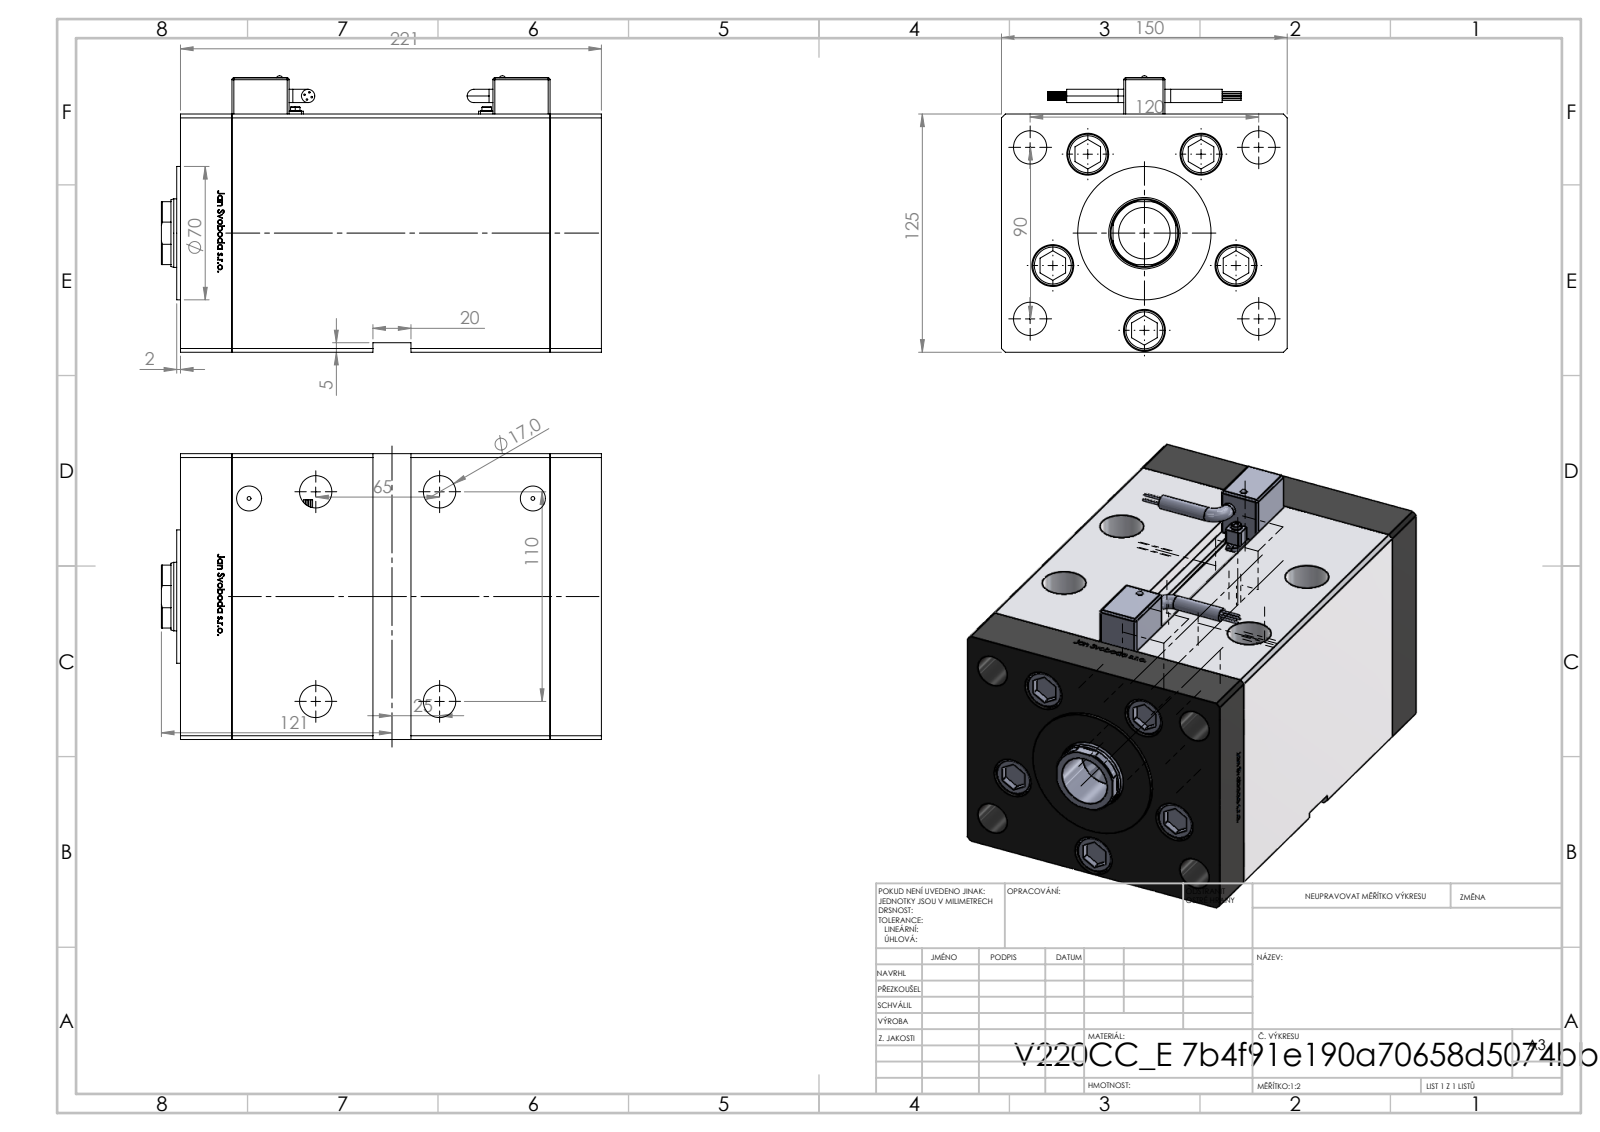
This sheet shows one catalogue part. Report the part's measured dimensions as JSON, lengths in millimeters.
{"part_name": "V220C_FRONT_E; Magnetic_Switch_MSU4; ALLEN BOLT; V220C BACK_E (+2 more)", "step_written_by": "SolidWorks 2019 (CONFIG_CONTROL_DESIGN)", "units": "millimeters", "bodies": {"solids": 16, "faces": 1410, "planar": 551, "cylindrical": 251, "other": 608}, "overall_size": [231, 150, 145.1], "volume_mm3": 3464000, "surface_area_mm2": 399924, "round_holes": [[17.5, 9], [22, 5], [17, 4], [23, 4], [2, 2], [3.6, 2], [5, 2], [7, 2], [13.16, 2], [27, 1], [36, 1], [37.5, 1]], "round_bosses_or_shafts": [[0.85, 8], [21, 5], [8, 5], [7, 4], [6, 2], [3.5, 2], [2.5, 2], [70, 1]], "partial_cylinders_radius": [[1, 24], [4, 4], [0.93, 2], [17.5, 1]], "face_to_face_distances": [167, 27, 194, 125, 150, 221, 100, 94, 120, 67], "hole_center_spacings": [51, 75, 8.25, 30.43, 30.48, 53.93, 56.04, 56.92]}
